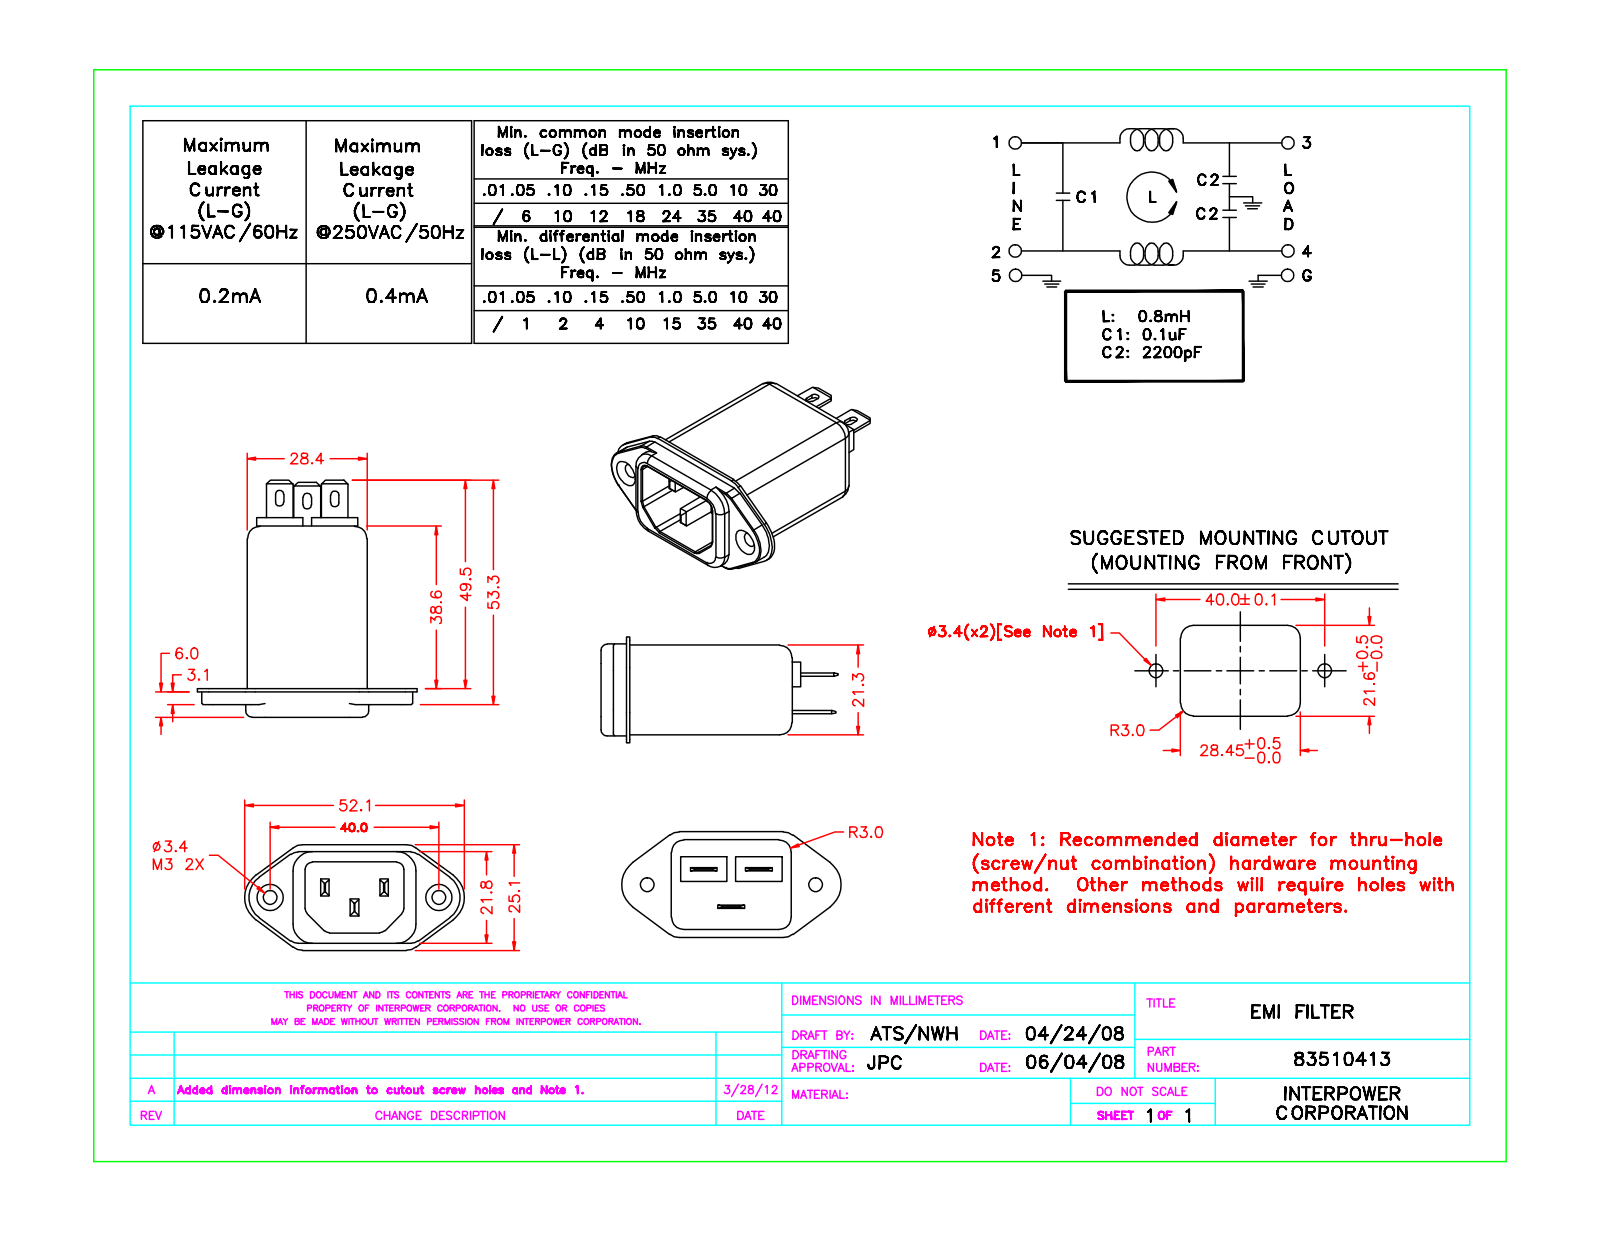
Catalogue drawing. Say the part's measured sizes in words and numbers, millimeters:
The part is named "06GEEG3E". Its 3-D file was written by "SolidWorks 2008 (CONFIG_CONTROL_DESIGN)". It is 1 solid with 191 faces: 103 planar, 63 cylindrical and 25 other. Overall it measures 56.3 by 52.1 by 25.1 millimeters. Its volume is 22 880 cubic millimeters and its surface area 8 548 square millimeters. Round holes: 2 of diameter 3.4. Partial cylindrical surfaces (rounded edges, fillets, slot ends): 12 of radius 0.3, 12 of radius 3, 6 of radius 1, 6 of radius 1.8, 4 of radius 1.5, 4 of radius 3.8, 4 of radius 4.6, 2 of radius 6. The main face-to-face distances are 21.3, 28.5, 2.2, 19.1, 9.7, 2.5, 26, 28.9, 38.6, 42.4. The hole center spacings are 40.
